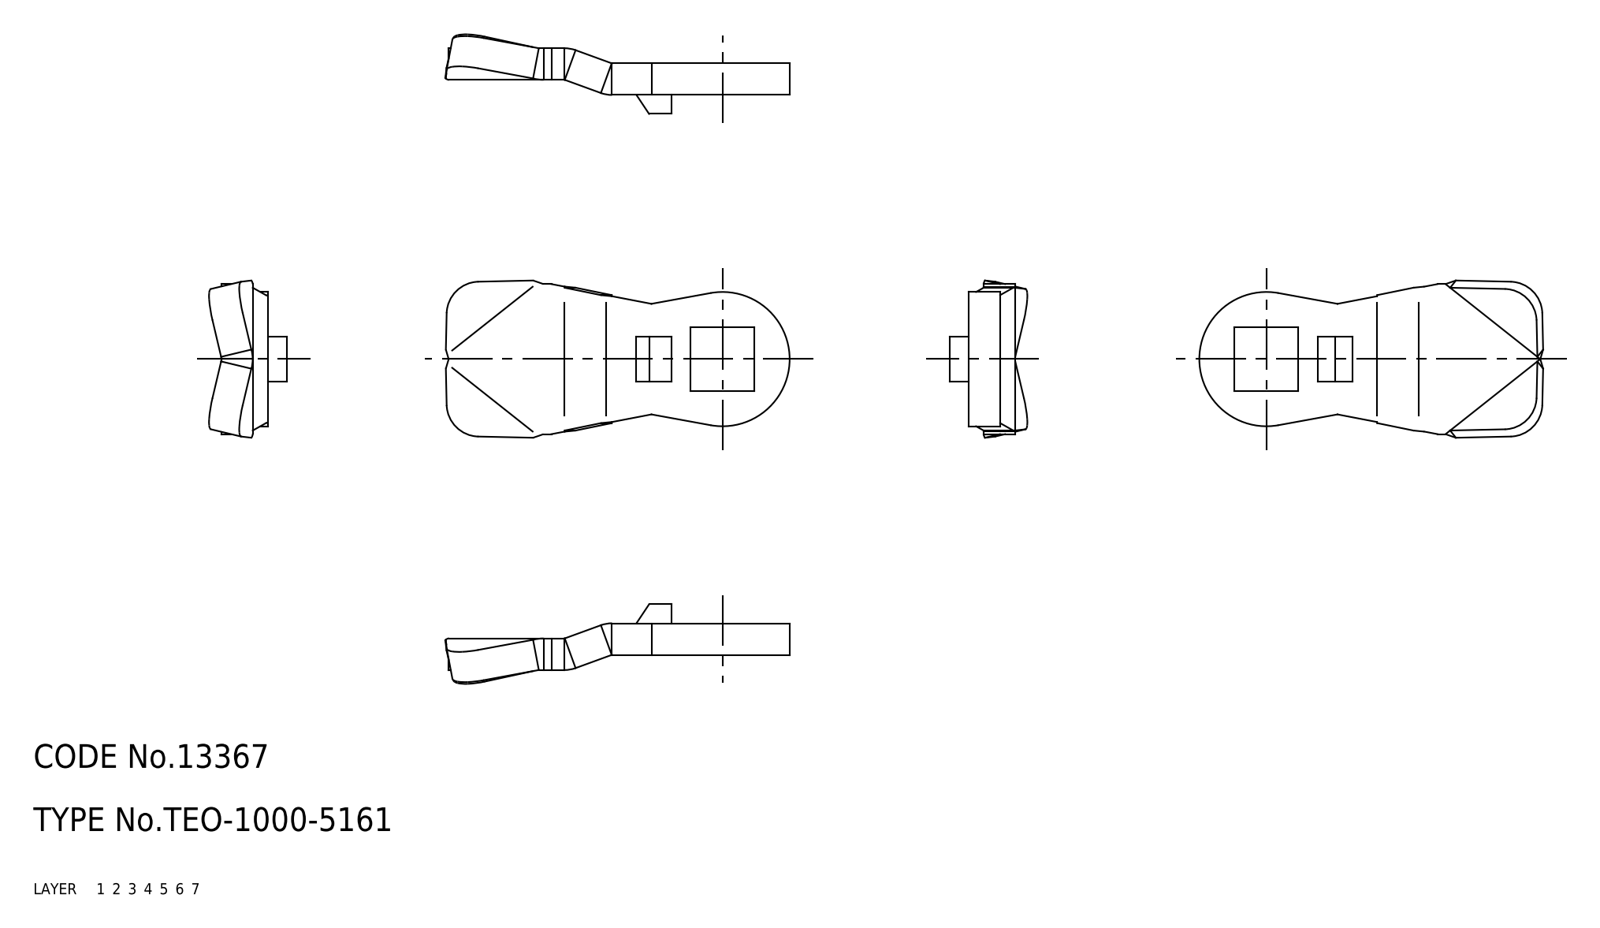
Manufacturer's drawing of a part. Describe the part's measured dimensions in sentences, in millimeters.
The part is named "cam". Its 3-D file was written by "CADfix (AUTOMOTIVE_DESIGN)". It is 1 solid with 47 faces: 0 planar, 0 cylindrical and 47 other. Overall it measures 44.17 by 21.07 by 12.03 millimeters. Its volume is 2 798 cubic millimeters and its surface area 2 096 square millimeters.
